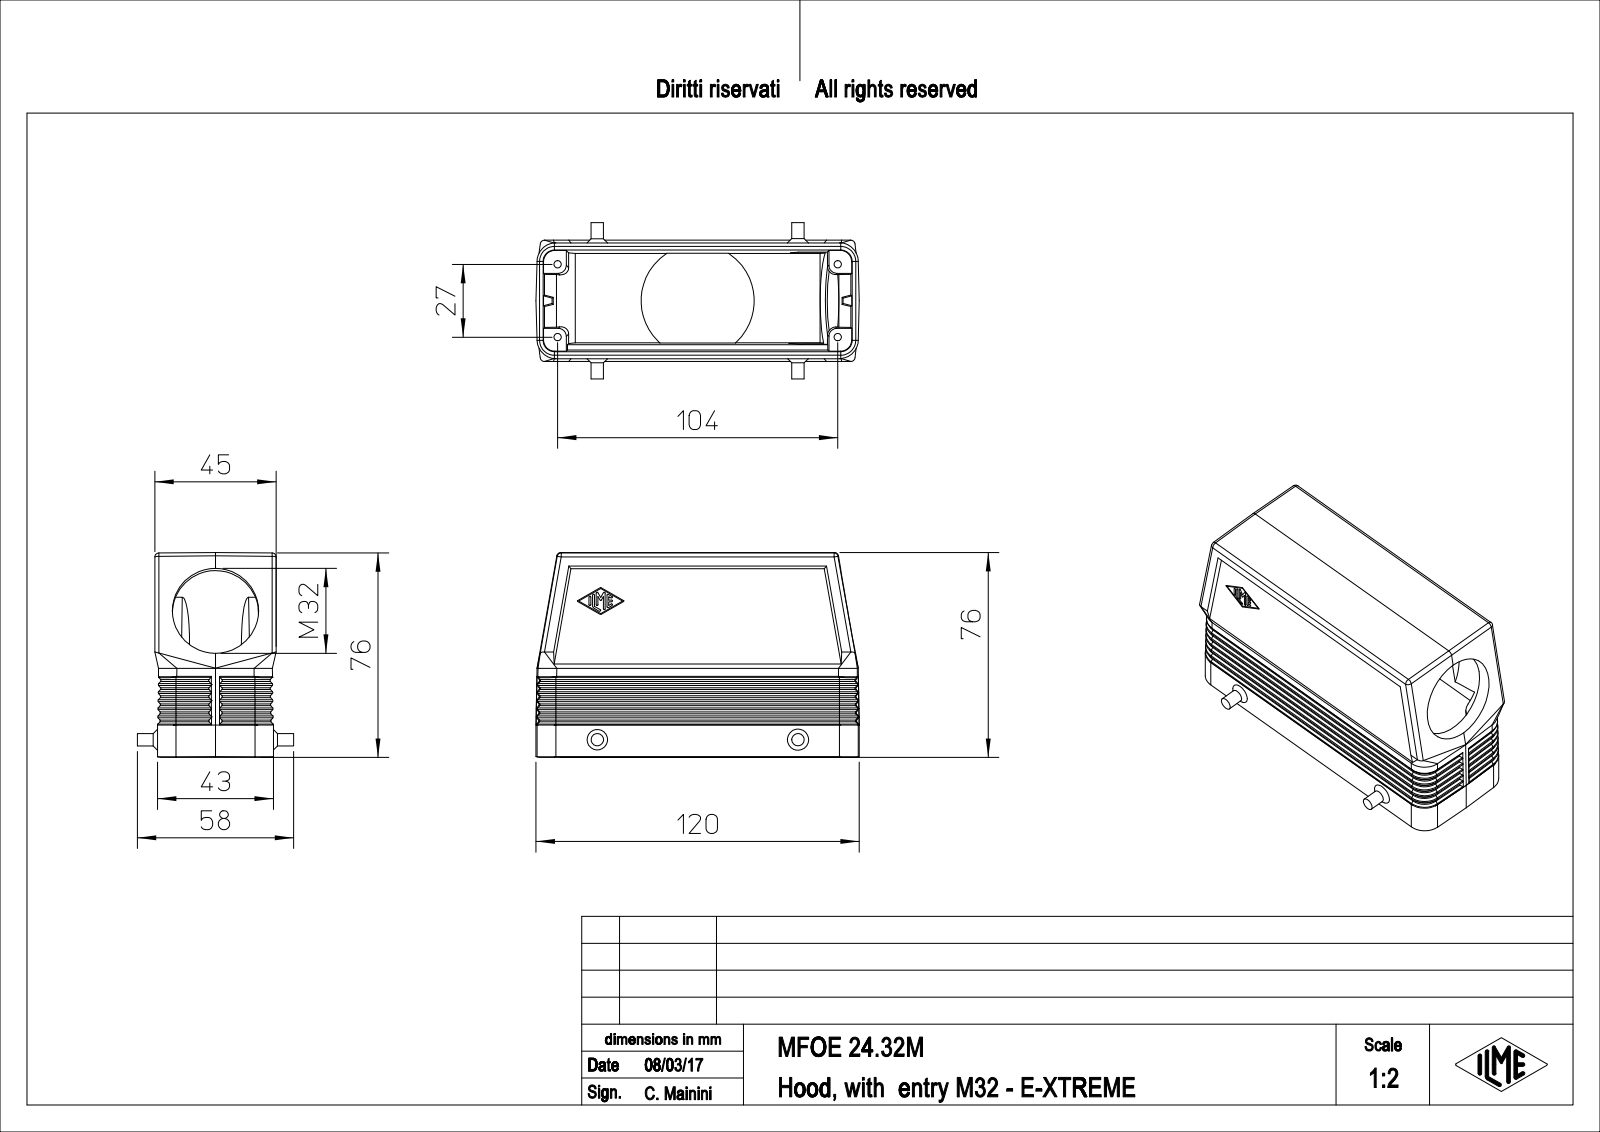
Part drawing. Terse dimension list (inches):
name: MFOE_24.32M
written by: PTC Creo Elements/Direct Modeling 19.0E 27-Jun-2016 (C) Parametric Technology GmbH (AUTOMOTIVE_DESIGN)
unit: in
bodies: 1 solid, 481 faces (211 planar, 134 cylindrical, 136 other)
size: 4.724 × 2.992 × 2.283
volume: 6.294 in³; area: 84.21 in²
holes: 4× ⌀0.108, 1× ⌀1.26, 1× ⌀1.575
bosses: 2× ⌀0.181
rounds: 78× R0.02, 10× R0.059, 8× R0.276, 4× R0.118, 4× R0.165, 1× R0.827
face distances: 1.693, 0.079, 0.079, 0.157, 0.126, 0.039, 1.732, 0.236, 0.333, 0.237
hole spacings: 1.063, 4.094, 4.23
